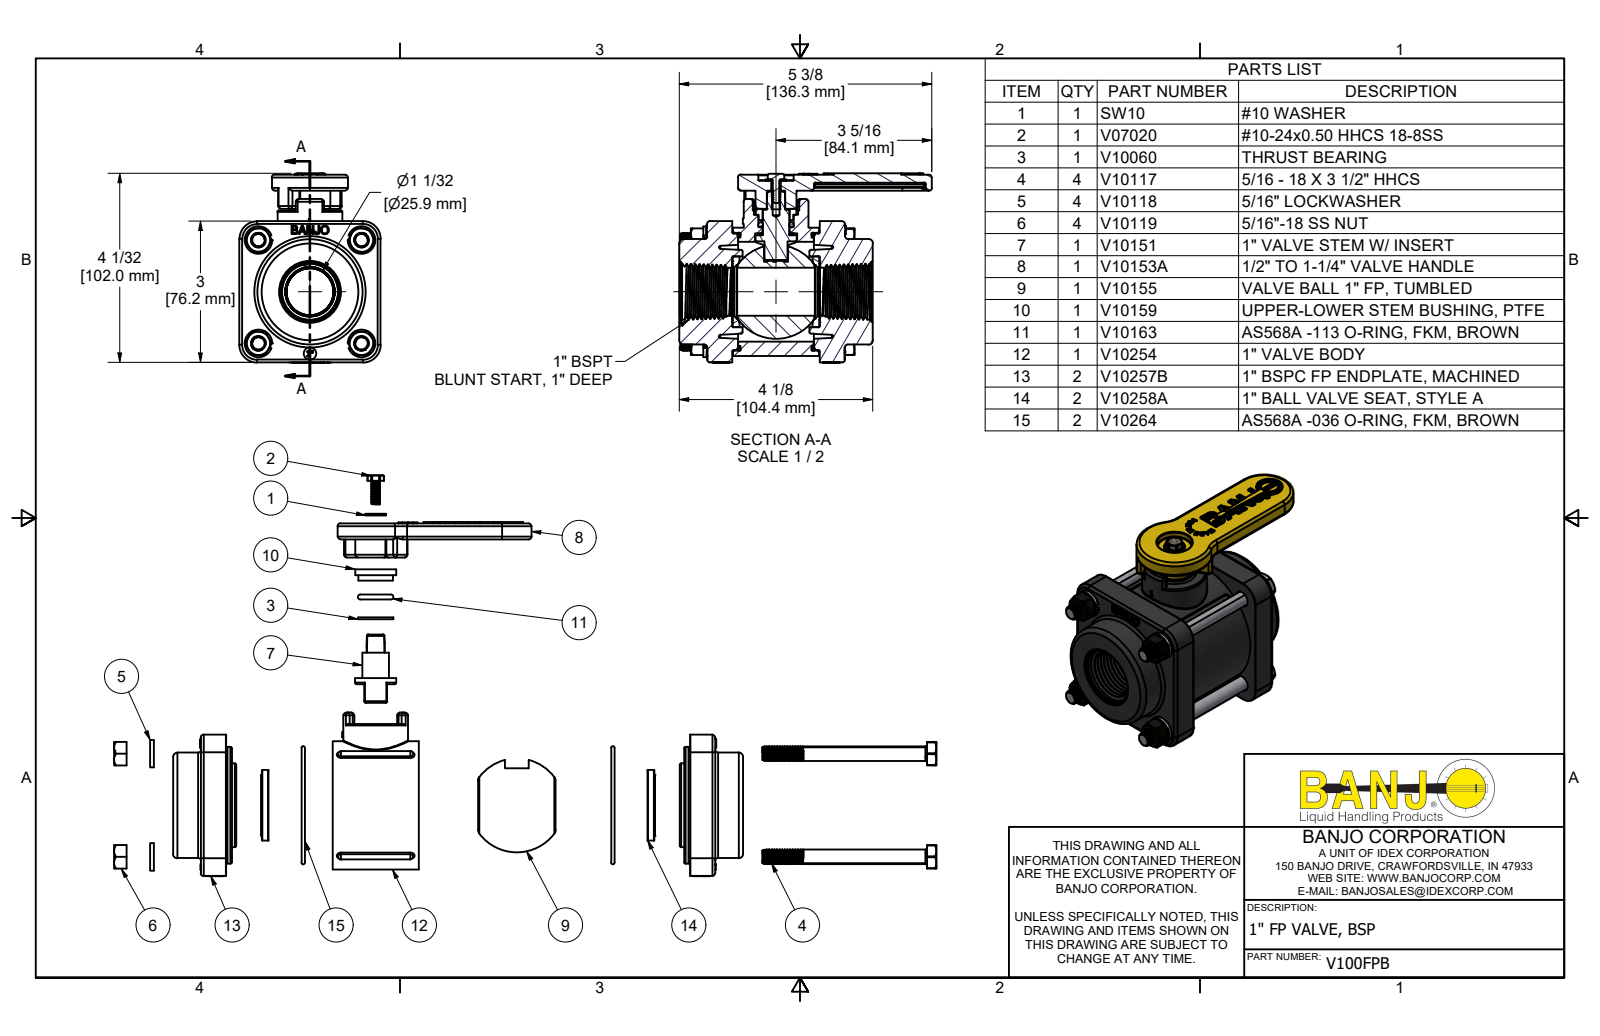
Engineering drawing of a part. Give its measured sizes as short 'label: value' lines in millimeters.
name: V100FPB; V10117; V10254; V10118 (+8 more)
written by: Autodesk Inventor 2022 (AUTOMOTIVE_DESIGN)
unit: mm
bodies: 29 solids, 3264 faces (1533 planar, 633 cylindrical, 1098 other)
size: 136.3 × 102.1 × 76.2
volume: 370 300 mm³; area: 126 800 mm²
holes: 4× ⌀6.4, 4× ⌀8.2, 4× ⌀8.9, 1× ⌀2.3, 1× ⌀3.7, 1× ⌀5.1, 1× ⌀5.2, 1× ⌀6.6, 1× ⌀9.6, 1× ⌀13.5, 1× ⌀14.3, 1× ⌀14.5
bosses: 60× ⌀6.8, 4× ⌀14.8, 4× ⌀8, 1× ⌀69.2, 1× ⌀62.9, 1× ⌀58.5, 1× ⌀56.9, 1× ⌀45.2
rounds: 66× R1.5, 32× R0.8, 12× R0.8, 8× R3.4, 4× R0.4, 4× R2, 4× R7.2, 4× R9.5
face distances: 31.8, 3.2, 76.2, 44.1, 28.6, 72.6, 75.8, 74.4, 60.8, 13.6
hole spacings: 39.4, 55.7, 28.4, 67.2, 78.7, 9.2, 33.3, 65.3
